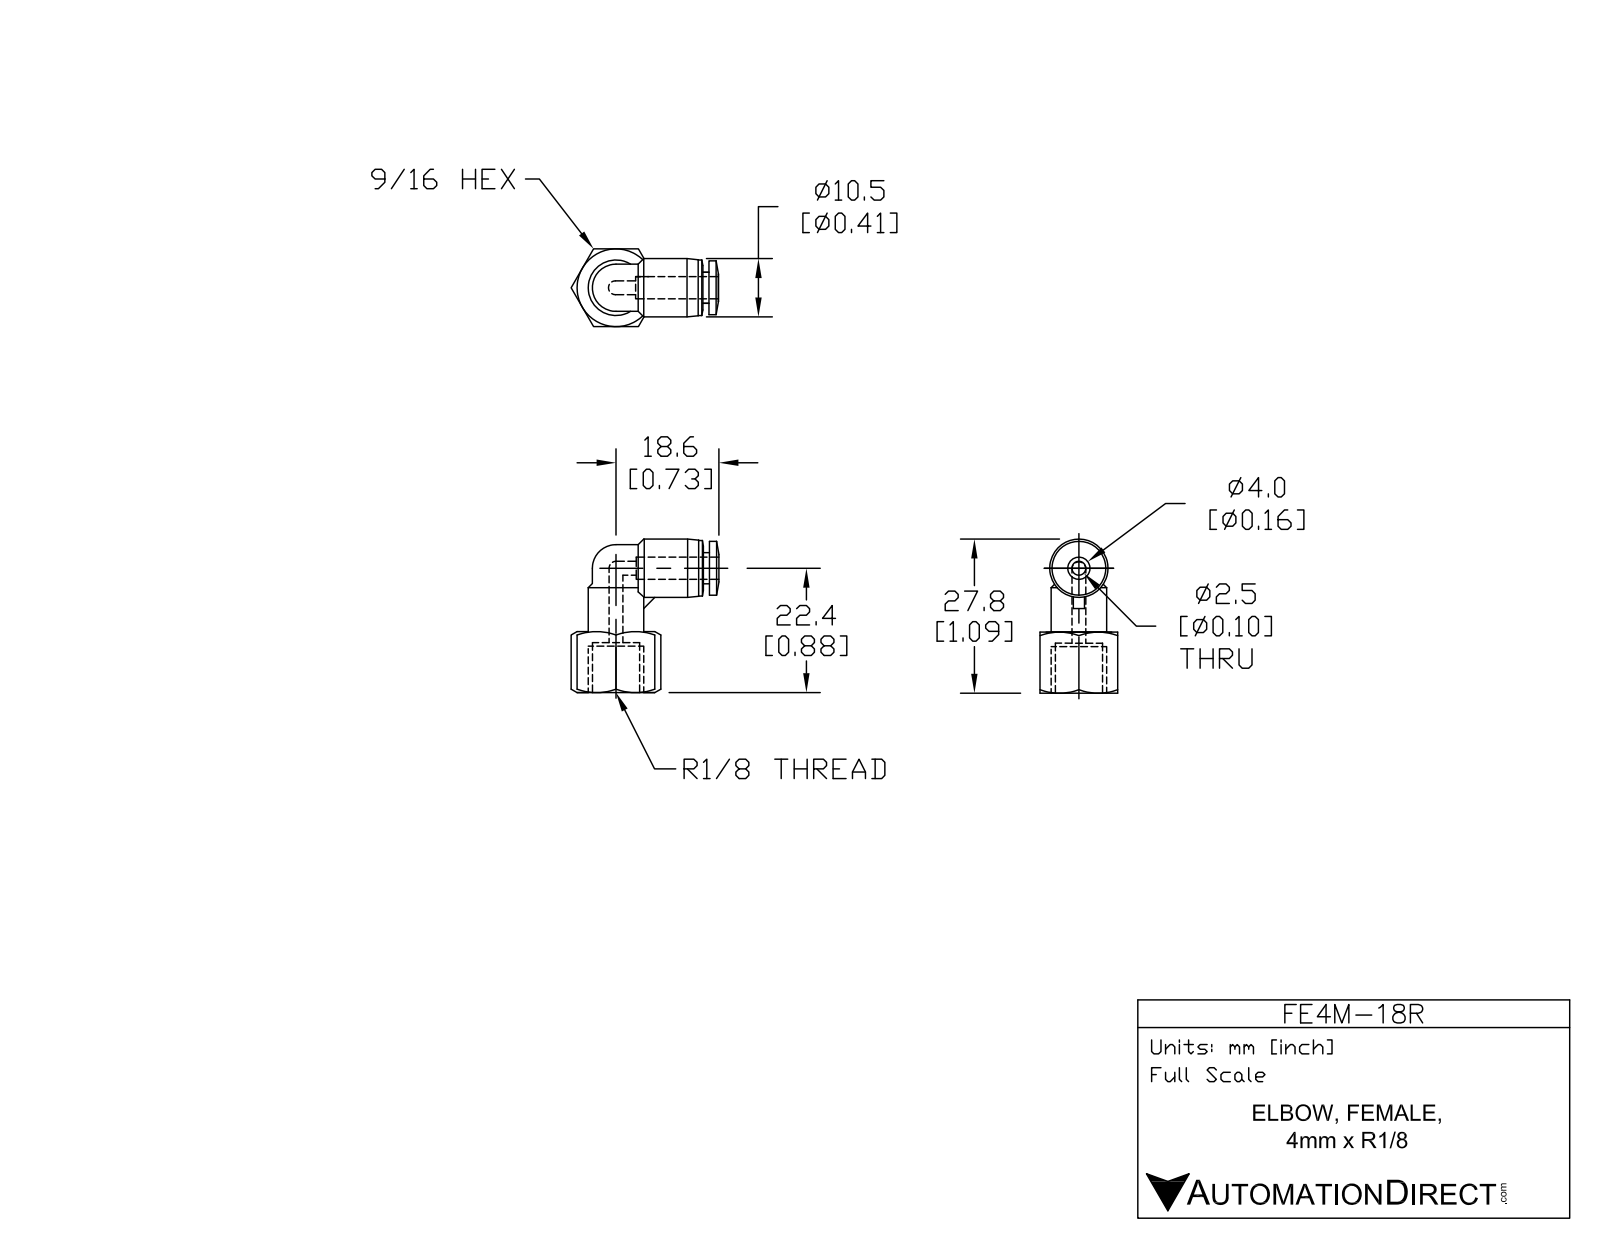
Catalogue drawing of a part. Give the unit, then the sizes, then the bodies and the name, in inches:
Units: inches
Overall size (bounding box): 1.093 × 1.045 × 0.551
Round holes (diameter × count): ⌀0.118 ×2, ⌀0.169 ×1
Round bosses / shafts (diameter × count): ⌀0.394 ×2, ⌀0.413 ×1, ⌀0.382 ×1, ⌀0.22 ×1
Partial cylindrical surfaces — rounded edges, fillets, slot ends (radius × count): R0.167 ×2
Main face-to-face distances: 0.551, 0.433, 0.079, 0.354, 0.043, 0.472, 0.516, 0.236, 0.315, 0.439
Volume: 0.186 in³ · Surface area: 3.785 in²
Bodies: 1 solid, 67 faces (17 planar, 19 cylindrical, 31 other)
Part name (STEP PRODUCT): FE4M-18R
STEP written by: SolidWorks 2015 (AUTOMOTIVE_DESIGN)
